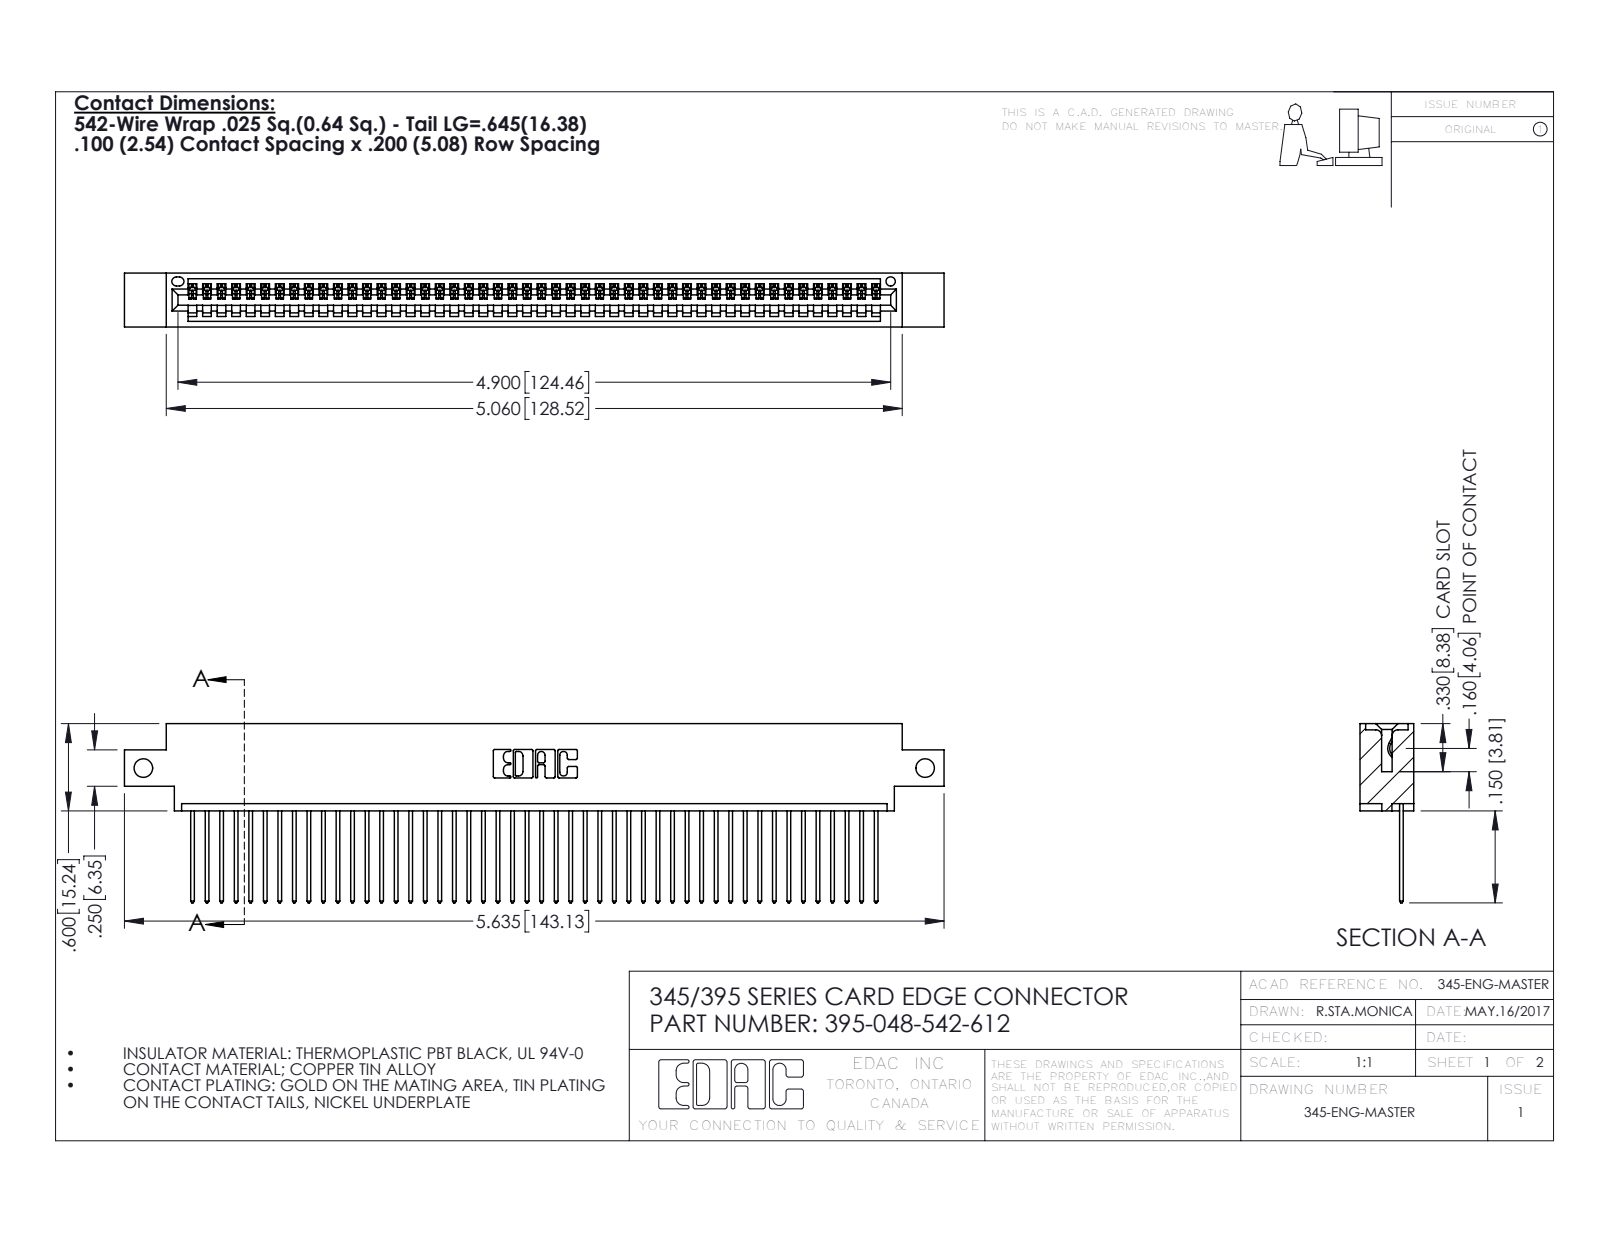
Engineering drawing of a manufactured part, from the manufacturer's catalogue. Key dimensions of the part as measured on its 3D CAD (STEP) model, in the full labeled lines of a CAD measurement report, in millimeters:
Part name (STEP PRODUCT): 395-048-542-612; 345-292-001_345-293-142; 345 Part_0.170 Offset - Side Mount
STEP written by: SolidWorks 2016 (CONFIG_CONTROL_DESIGN)
Units: millimetres
Bodies: 49 solids, 2914 faces (2004 planar, 910 cylindrical, 0 other)
Overall size (bounding box): 143.1 × 31.3 × 9.4
Volume: 13 600 mm³ · Surface area: 18 750 mm²
Round holes (diameter × count): ⌀3.3 ×2, ⌀1.6 ×1
Partial cylindrical surfaces — rounded edges, fillets, slot ends (radius × count): R0.2 ×96, R0.3 ×96, R0.3 ×22, R0.2 ×6, R0.8 ×6, R0.7 ×3, R0.8 ×2, R1 ×2
Main face-to-face distances: 1.8, 7.6, 9.4, 2.5, 6.9, 0.6, 5.1, 5.7, 4.4, 3.8
Hole centre spacings: 136.5
